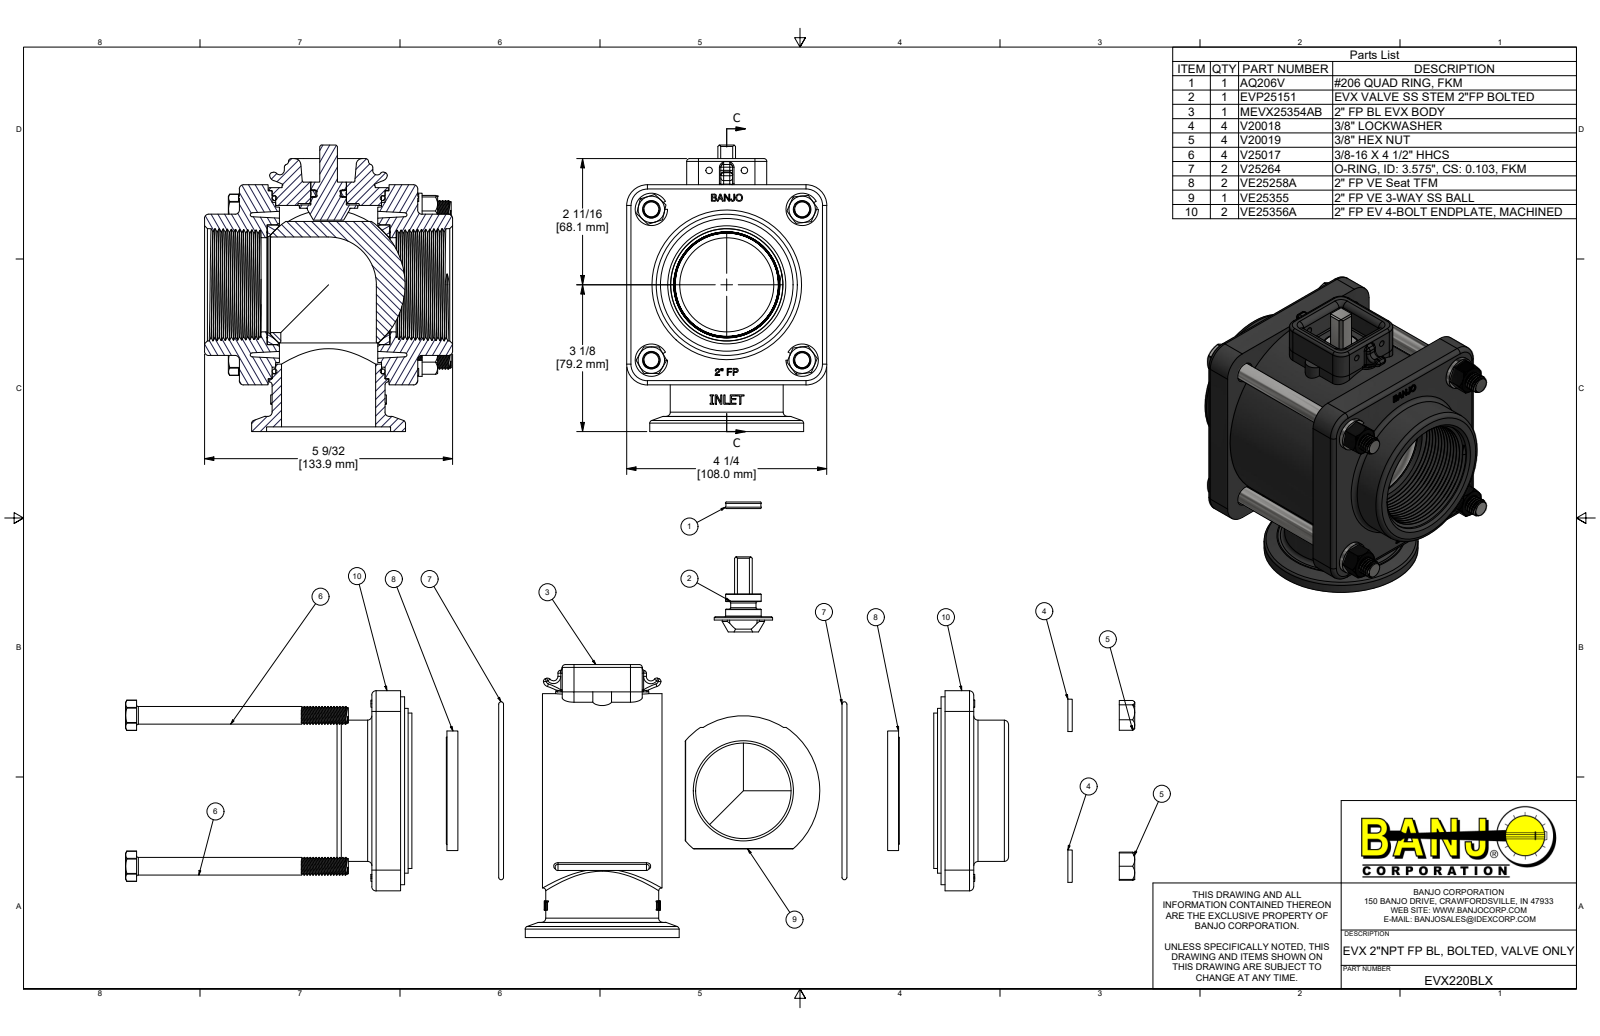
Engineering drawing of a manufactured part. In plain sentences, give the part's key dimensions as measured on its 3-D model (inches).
The part is named "EVX220BLX; MEVX25354AB; MEVX25354ABX; V25017 (+8 more)". Its 3-D file was written by "Autodesk Inventor 2019 (AUTOMOTIVE_DESIGN)". It is 22 solids with 1433 faces: 486 planar, 396 cylindrical and 551 other. Overall it measures 6.086 by 5.27 by 4.25 inches. Its volume is 67.43 cubic inches and its surface area 385.3 square inches. Round holes: 4 of diameter 0.307, 4 of diameter 0.385, 4 of diameter 0.438, 3 of diameter 2.03, 2 of diameter 0.135, 2 of diameter 2, 1 of diameter 0.76, 1 of diameter 1.3, 1 of diameter 2.045, 1 of diameter 2.545, 1 of diameter 2.635, 1 of diameter 3.37. Round bosses or shafts: 60 of diameter 0.324, 4 of diameter 0.687, 4 of diameter 0.375, 1 of diameter 4.125, 1 of diameter 3.99, 1 of diameter 3.5, 1 of diameter 3.3, 1 of diameter 3.27. Partial cylindrical surfaces (rounded edges, fillets, slot ends): 24 of radius 0.06, 12 of radius 0.03, 10 of radius 0.09, 8 of radius 0.062, 8 of radius 0.162, 6 of radius 0.125, 4 of radius 0.02, 4 of radius 0.21. The main face-to-face distances are 0.61, 3.18, 3.79, 0.695, 3.095, 0.085, 2.485, 4.25, 0.16, 0.77. The hole center spacings are 2.265, 3.204, 1.48, 2.143, 2.458, 4.214, 4.49, 4.531.
